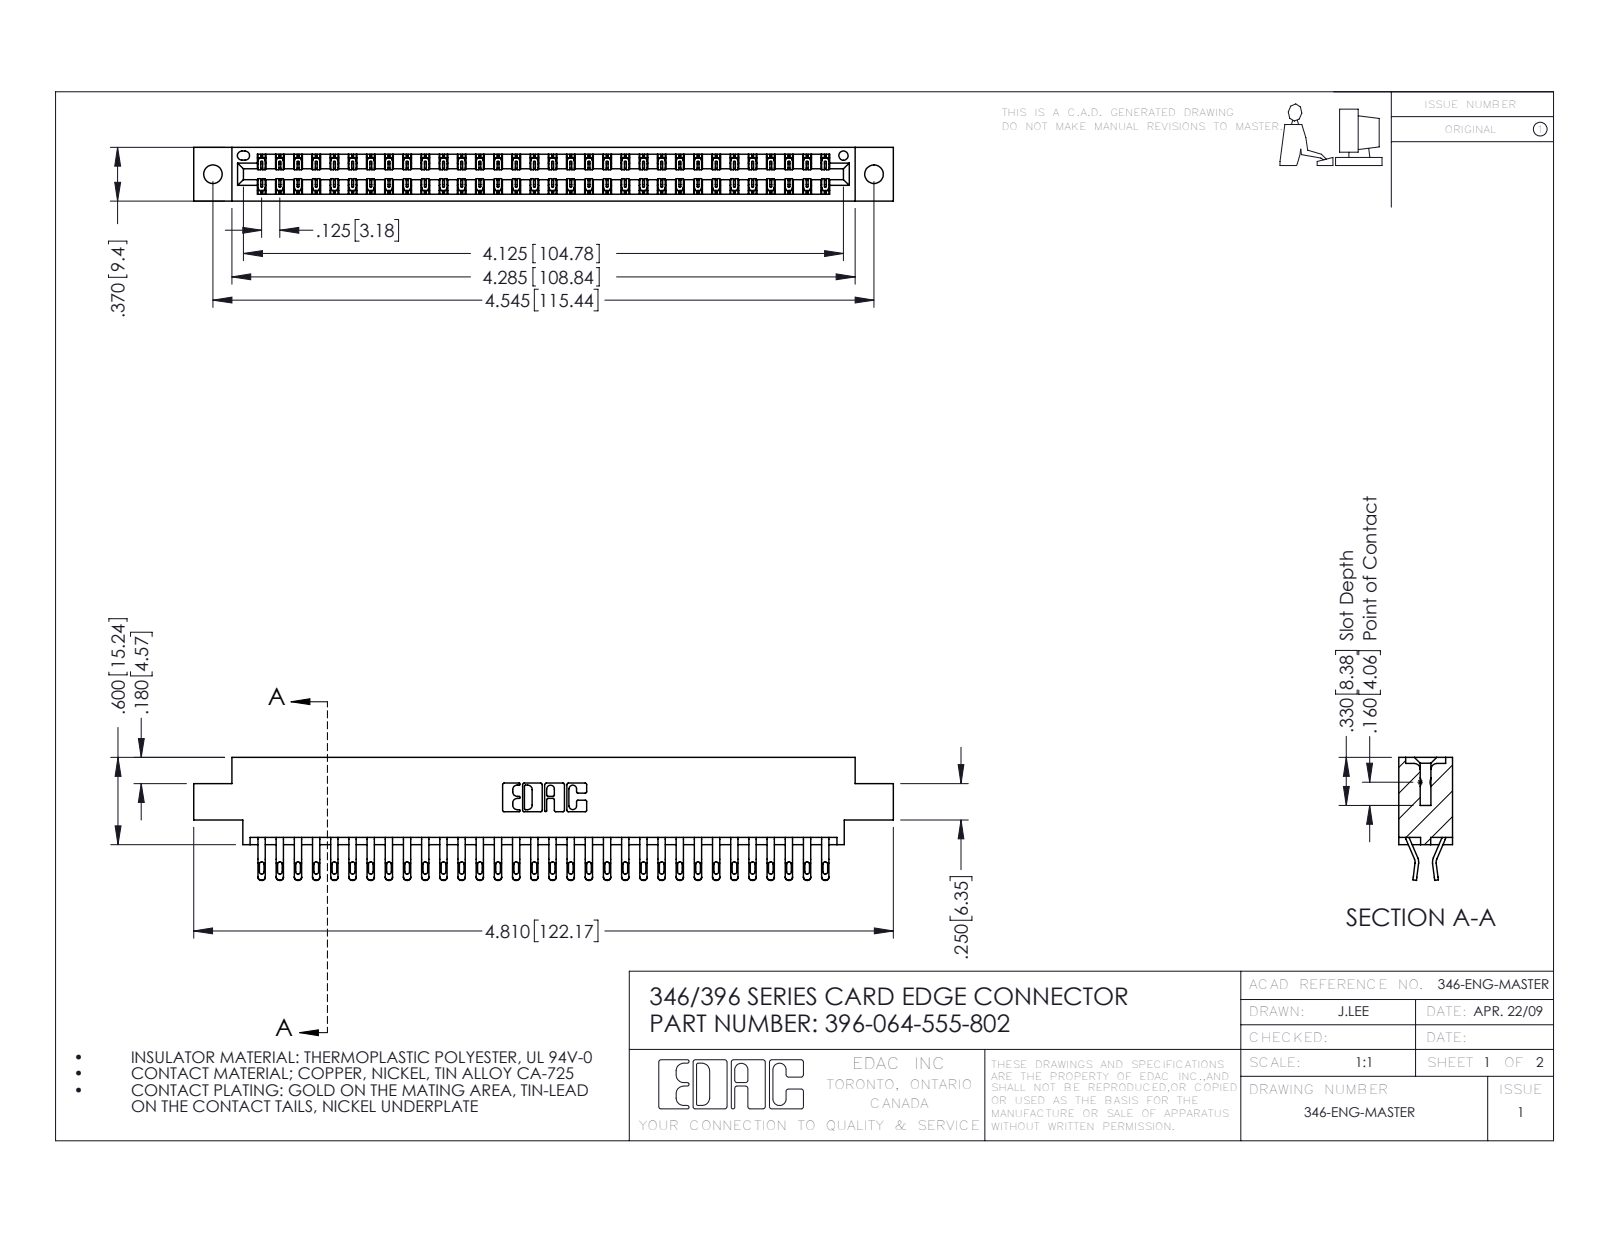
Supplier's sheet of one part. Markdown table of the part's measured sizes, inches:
| quantity | value |
| --- | --- |
| part name | 345-292-001_555 Tail; 346 Part_0.170 Offset - 0.128 Dia; 396-064-555-802 |
| STEP written by | SolidWorks 2016 (CONFIG_CONTROL_DESIGN) |
| units | inches |
| bodies | 65 solids, 3838 faces (2192 planar, 1646 cylindrical, 0 other) |
| overall size | 4.81 × 0.845 × 0.37 |
| volume | 0.722 in³ |
| surface area | 25.85 in² |
| round holes (diameter × count) | 0.128 × 2, 0.064 × 1 |
| partial cylindrical surfaces (radius × count) | 0.016 × 128, 0.02 × 128, 0.006 × 96, 0.01 × 22, 0.007 × 6, 0.031 × 6, 0.026 × 3, 0.01 × 2 |
| main face-to-face distances | 0.048, 0.322, 0.37, 0.25, 0.025, 0.072, 0.298, 0.275, 0.148, 0.222 |
| hole center spacings | 0.246, 4.337, 4.545 |
